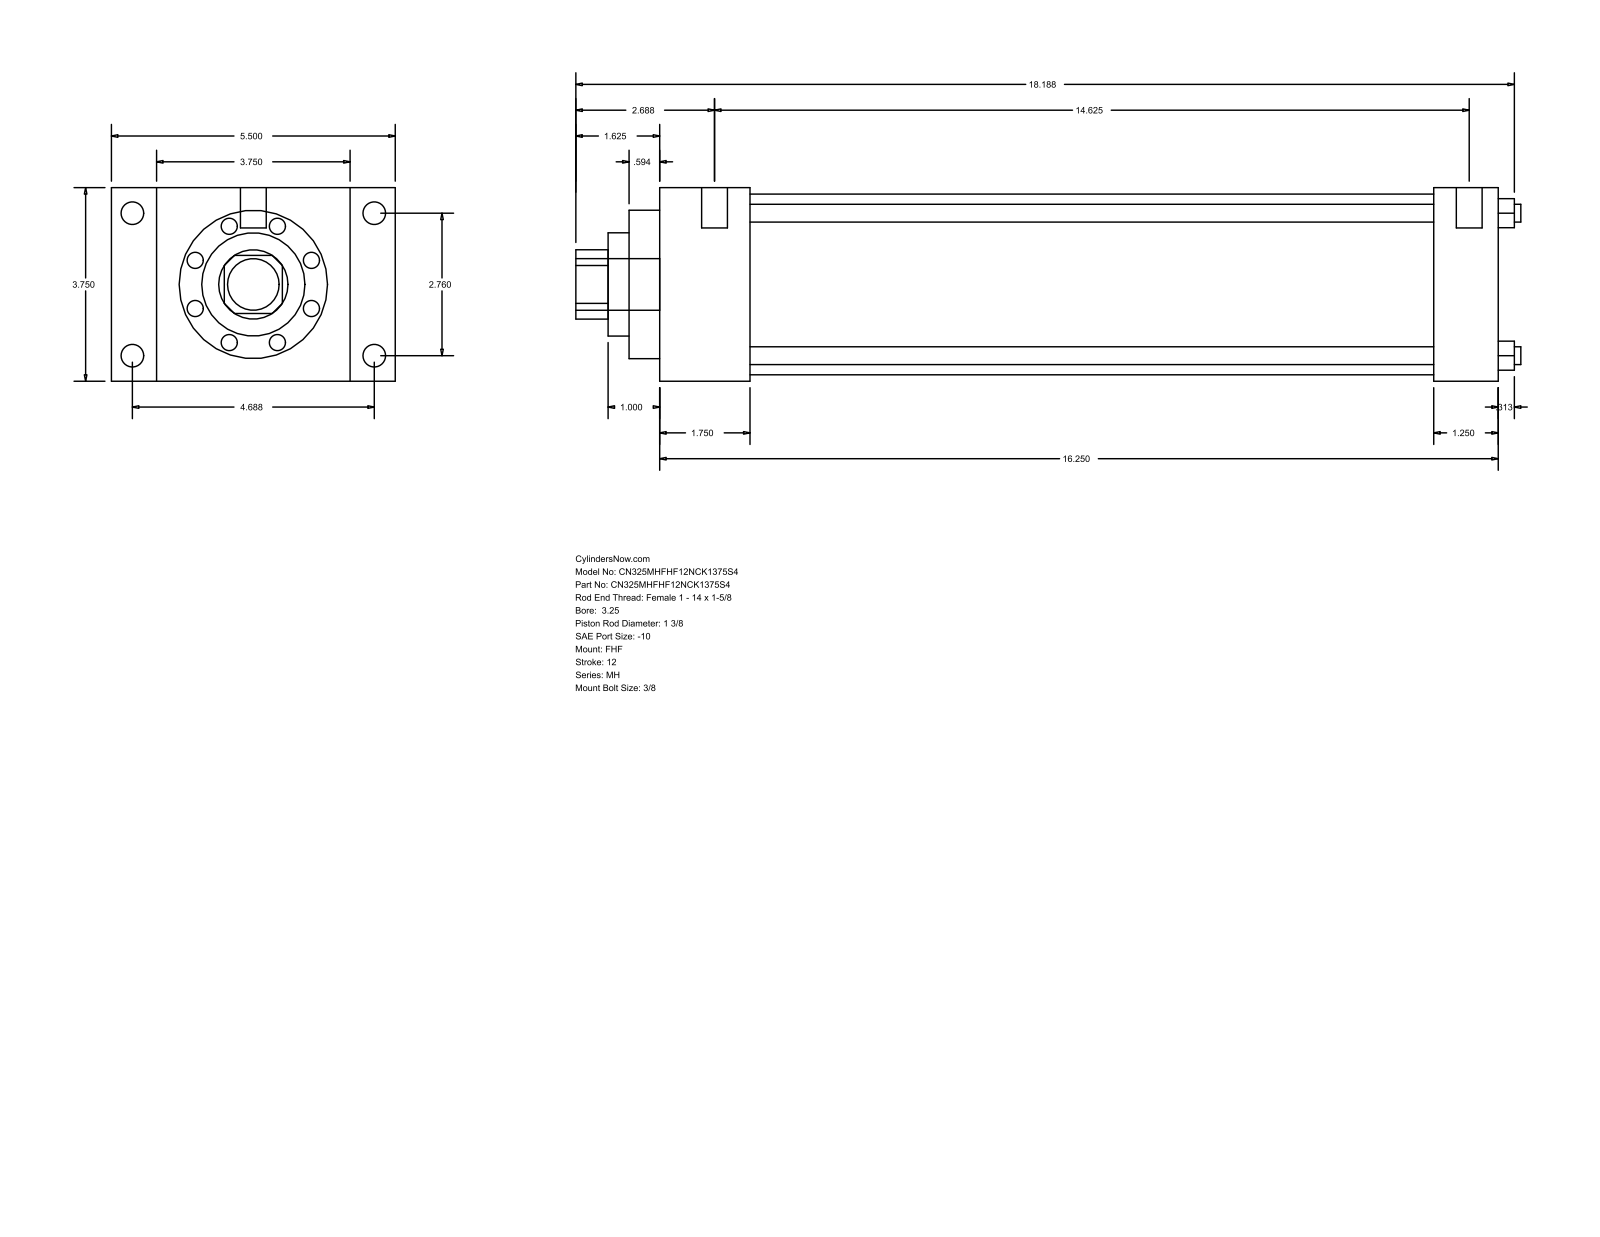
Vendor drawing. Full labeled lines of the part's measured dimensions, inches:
Part name (STEP PRODUCT): MH_FHF__0325_1.375
STEP written by: GSSL Pune (CONFIG_CONTROL_DESIGN)
Units: inches
Bodies: 0 solids, 90 faces (61 planar, 29 cylindrical, 0 other)
Overall size (bounding box): 18.313 × 5.5 × 3.75
Round holes (diameter × count): ⌀0.345 ×4, ⌀1.375 ×1, ⌀2 ×1, ⌀2.875 ×1, ⌀3.5 ×1
Round bosses / shafts (diameter × count): ⌀0.438 ×4, ⌀0.219 ×4, ⌀0.5 ×2, ⌀1 ×1
Partial cylindrical surfaces — rounded edges, fillets, slot ends (radius × count): R0.672 ×1
Main face-to-face distances: 3.75, 16.25, 1.75, 14.5, 0.875, 4.625, 5.5, 15, 13.25, 1.25
Hole centre spacings: 1.952, 2.76, 3.903
